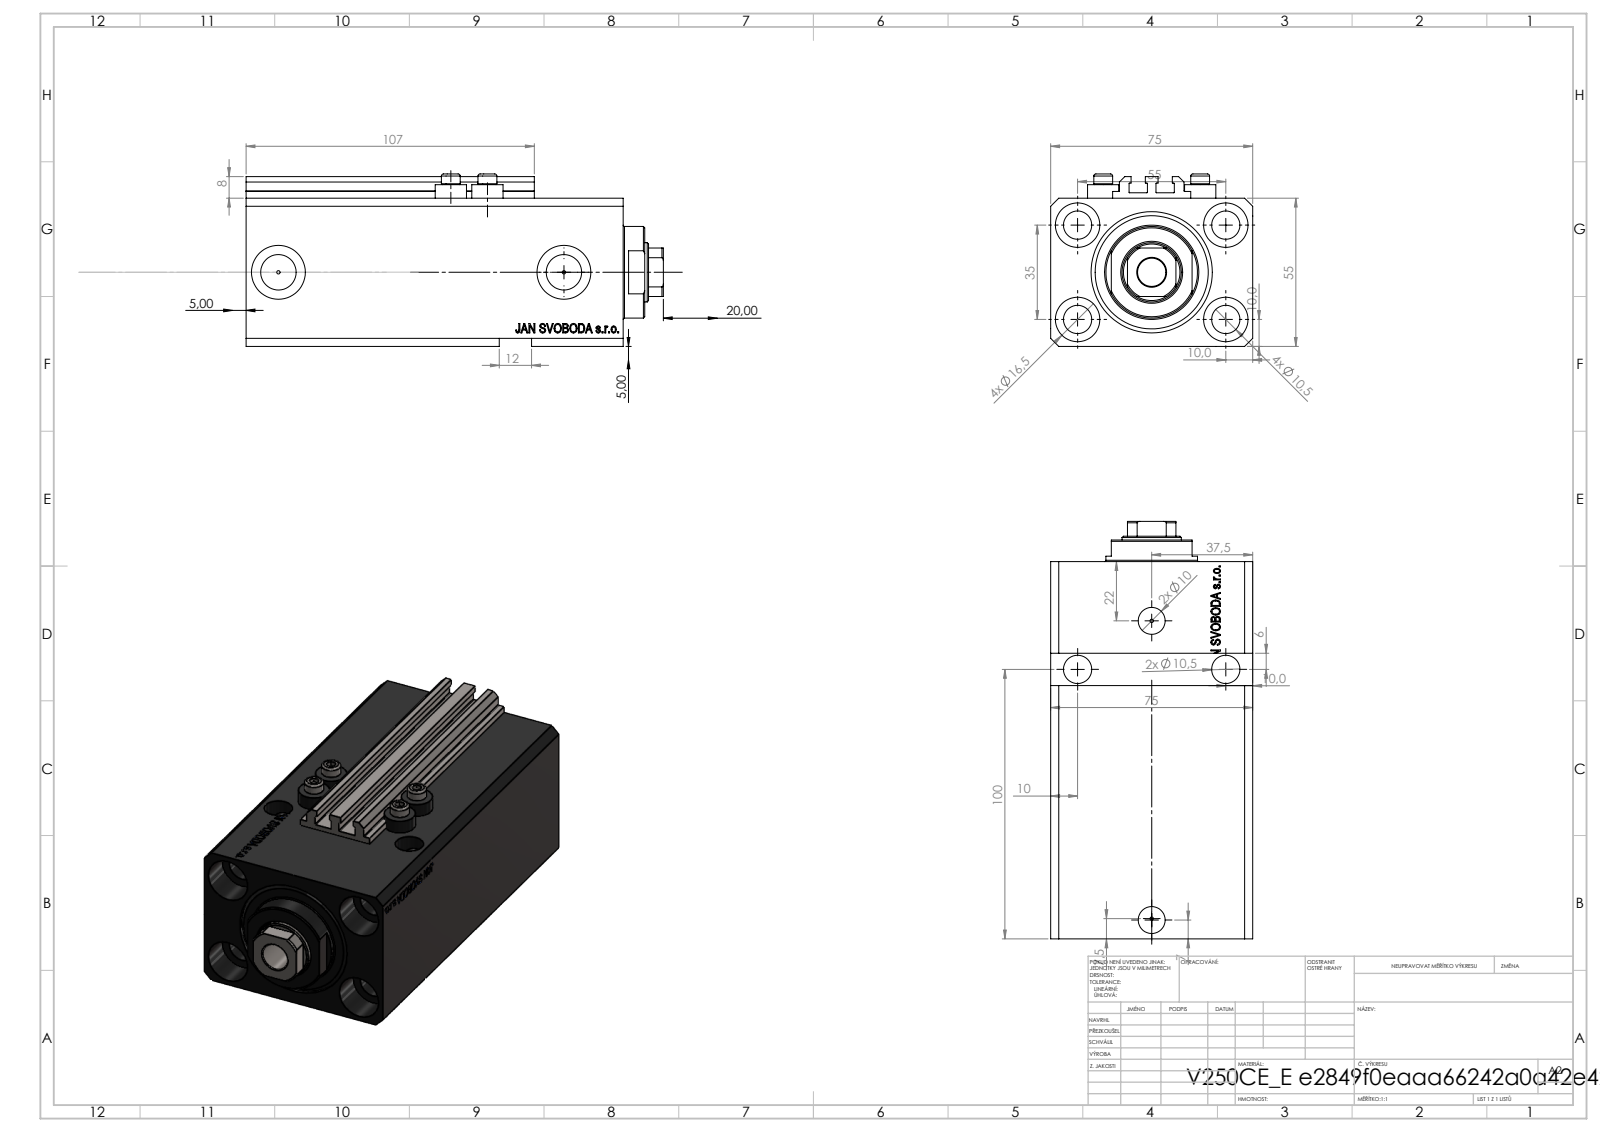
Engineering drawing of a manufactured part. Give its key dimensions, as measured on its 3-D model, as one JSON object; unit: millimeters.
{"part_name": "V250CE_E; V250CE_VC_E; V250CE_C_VCP; ALLEN BOLT V250CE", "step_written_by": "SolidWorks 2019 (CONFIG_CONTROL_DESIGN)", "units": "millimeters", "bodies": {"solids": 8, "faces": 1064, "planar": 514, "cylindrical": 126, "other": 424}, "overall_size": [154.9, 75, 64], "volume_mm3": 491635, "surface_area_mm2": 116388, "round_holes": [[10.5, 7], [1.25, 4], [4, 4], [16.5, 4], [10, 2], [13.16, 2], [20, 2], [22, 1], [32, 1], [45, 1]], "round_bosses_or_shafts": [[11.6, 4], [7, 4], [34, 1]], "partial_cylinders_radius": [[0.2, 10], [10.5, 1]], "face_to_face_distances": [55, 75, 140, 112.9, 27.1, 3, 9.9, 57, 103, 130.1], "hole_center_spacings": [32.6, 55, 13.6, 14.09, 25.81, 32.87, 33.62, 35]}
